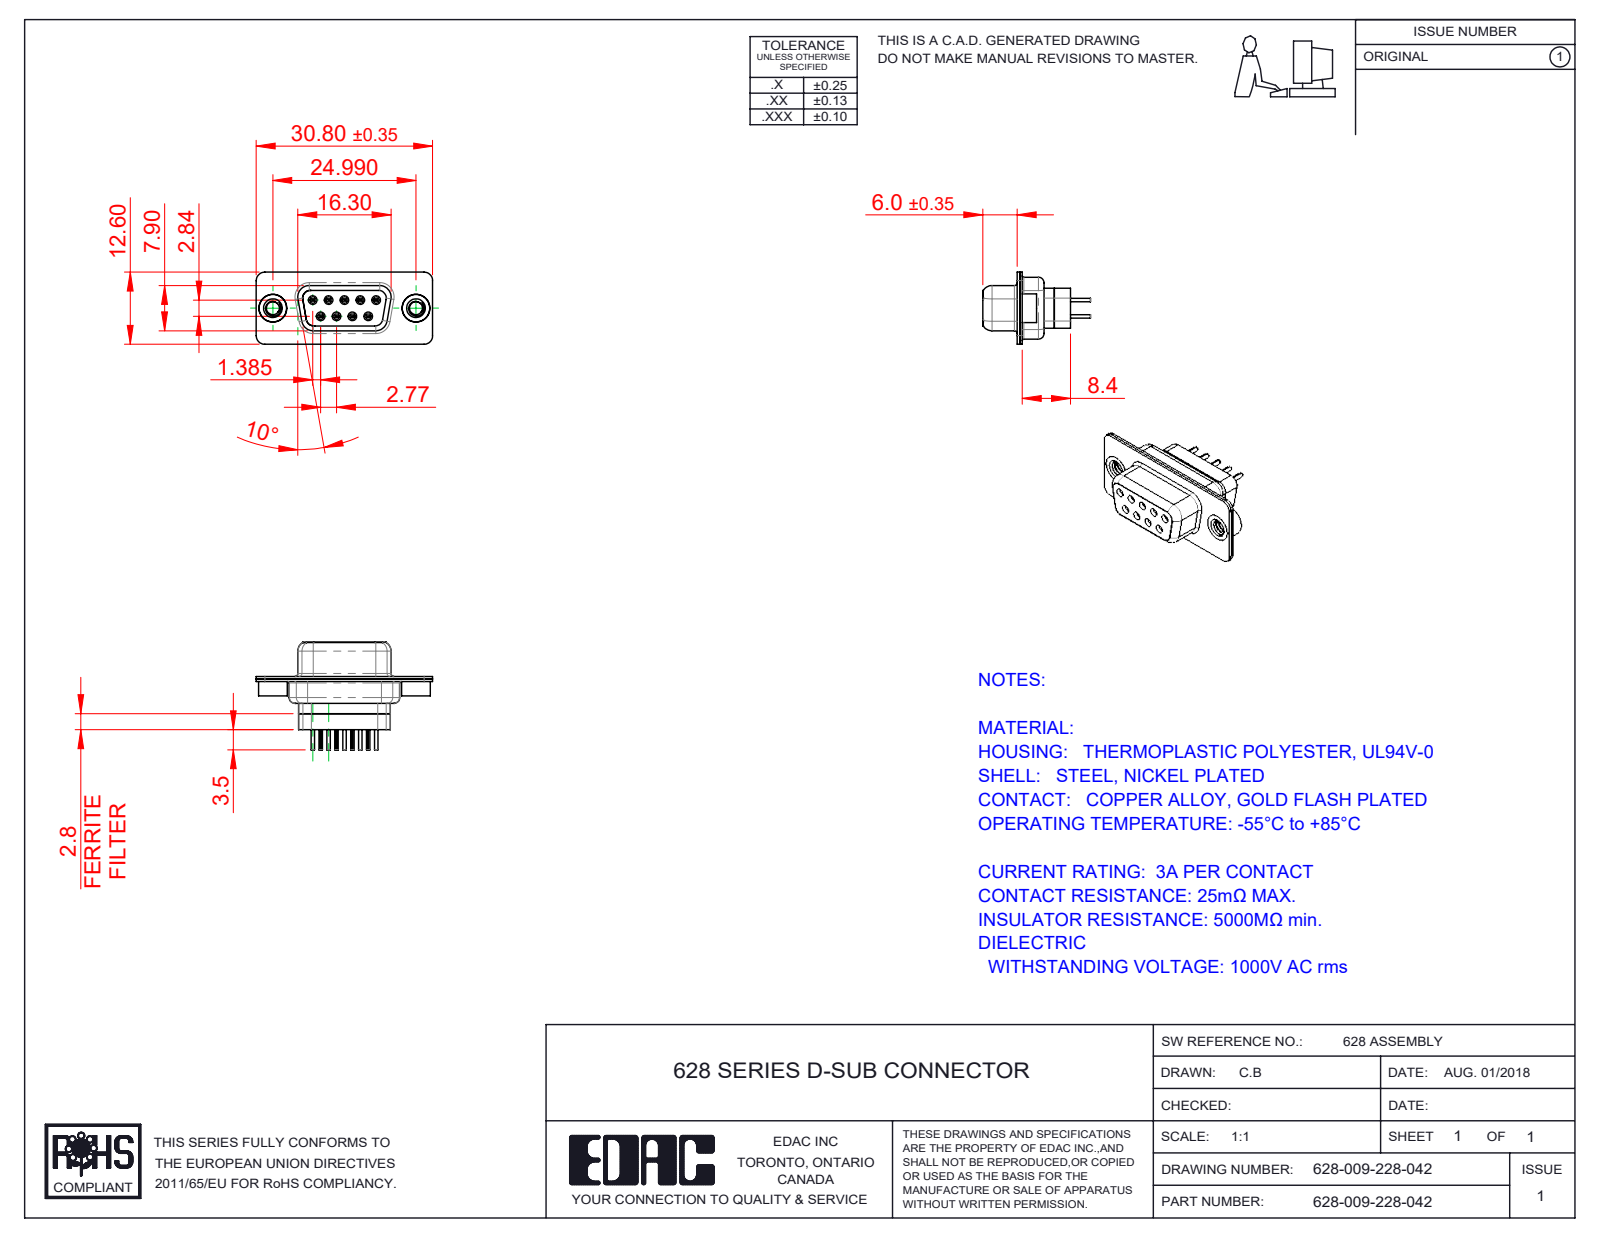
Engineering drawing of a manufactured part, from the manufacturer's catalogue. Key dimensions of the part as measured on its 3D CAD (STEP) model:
Part name (STEP PRODUCT): 628 Housing_09 FF; 628 4-40 Threaded Rivet; 628 Shell Front_09 Contacts; 628 Shell Rear_09 Contacts (+3 more)
STEP written by: SolidWorks 2020 (CONFIG_CONTROL_DESIGN)
Units: millimetres
Bodies: 15 solids, 1447 faces (352 planar, 455 cylindrical, 640 other)
Overall size (bounding box): 30.8 × 18.8 × 12.6
Volume: 1 997 mm³ · Surface area: 4 957 mm²
Round holes (diameter × count): ⌀0.2 ×9, ⌀0.8 ×9, ⌀0.9 ×9, ⌀1.1 ×9, ⌀1.6 ×9, ⌀1.7 ×5, ⌀2.26 ×2, ⌀4 ×2, ⌀4.05 ×2, ⌀4.85 ×2
Round bosses / shafts (diameter × count): ⌀2 ×9, ⌀1.5 ×9, ⌀1.2 ×9, ⌀0.6 ×9, ⌀5 ×2, ⌀4.95 ×2, ⌀4.8 ×2
Partial cylindrical surfaces — rounded edges, fillets, slot ends (radius × count): R0.1 ×18, R1.5 ×17, R2 ×12, R0.28 ×9, R1.35 ×6, R0.25 ×4, R0.5 ×4, R0.6 ×4
Main face-to-face distances: 0.45, 0.4, 0.9, 6.05, 6.5, 5.6, 8.85, 6.6, 8.4, 8.5
Hole centre spacings: 3.16, 2.77, 5.54, 5.03, 5.04, 8.31, 7.48, 7.49
